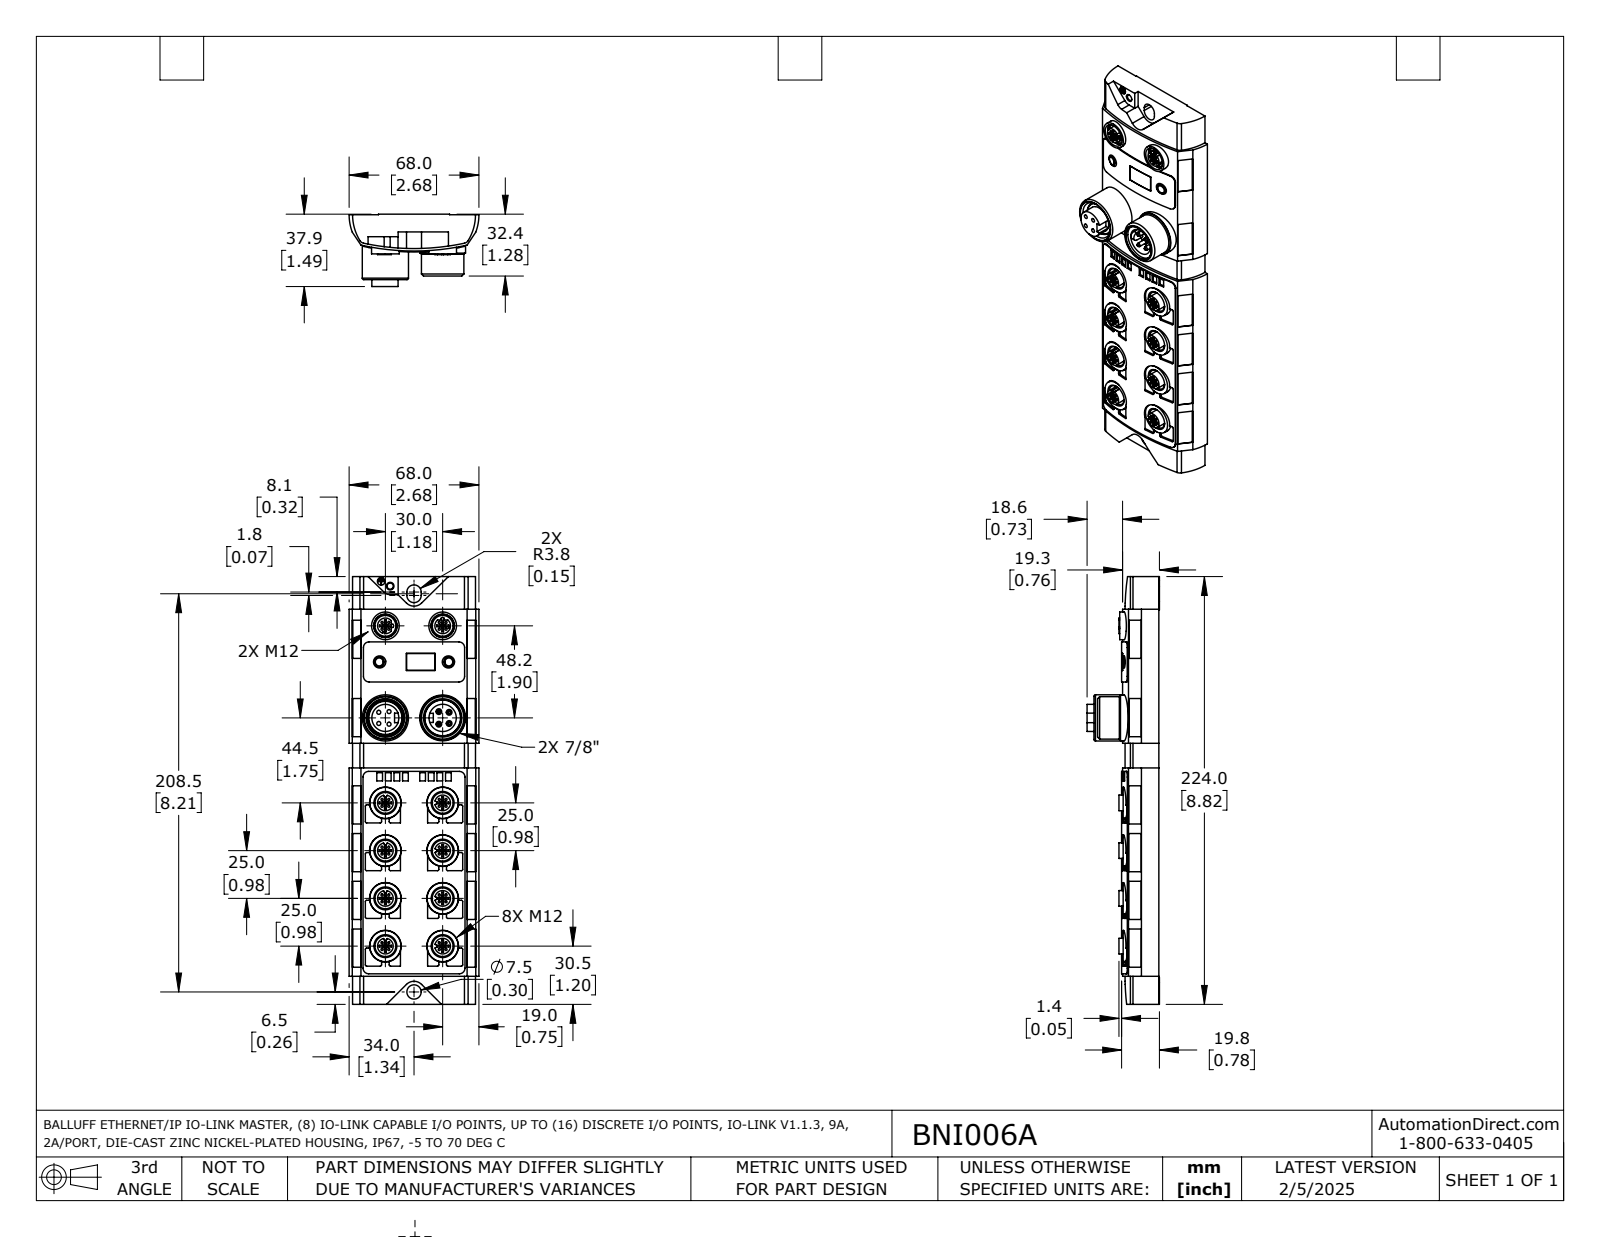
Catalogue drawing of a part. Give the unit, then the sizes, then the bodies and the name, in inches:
Units: inches
Overall size (bounding box): 8.819 × 2.677 × 1.492
Round holes (diameter × count): ⌀0.043 ×50, ⌀0.43 ×10, ⌀0.654 ×8, ⌀0.083 ×4, ⌀0.484 ×2, ⌀0.128 ×1, ⌀0.157 ×1, ⌀0.295 ×1, ⌀0.563 ×1, ⌀0.736 ×1, ⌀0.798 ×1
Round bosses / shafts (diameter × count): ⌀0.643 ×8, ⌀0.323 ×8, ⌀0.118 ×4, ⌀0.078 ×4, ⌀0.571 ×2, ⌀0.953 ×1, ⌀0.945 ×1, ⌀0.875 ×1
Partial cylindrical surfaces — rounded edges, fillets, slot ends (radius × count): R0.028 ×80, R0.031 ×48, R0.008 ×16, R0.117 ×6, R0.118 ×3, R0.047 ×2, R0.114 ×2, R0.148 ×2
Main face-to-face distances: 0.736, 8.819, 0.748, 0.118, 0.087, 0.283, 0.551, 0.539, 0.197, 0.122
Hole centre spacings: 0.098, 0.139, 1.056, 0.917, 1.537, 0.984, 1.181, 1.969
Volume: 15.58 in³ · Surface area: 84.81 in²
Bodies: 1 solid, 1095 faces (591 planar, 450 cylindrical, 54 other)
Part name (STEP PRODUCT): BNI006A
STEP written by: SolidWorks 2021 (AUTOMOTIVE_DESIGN)
